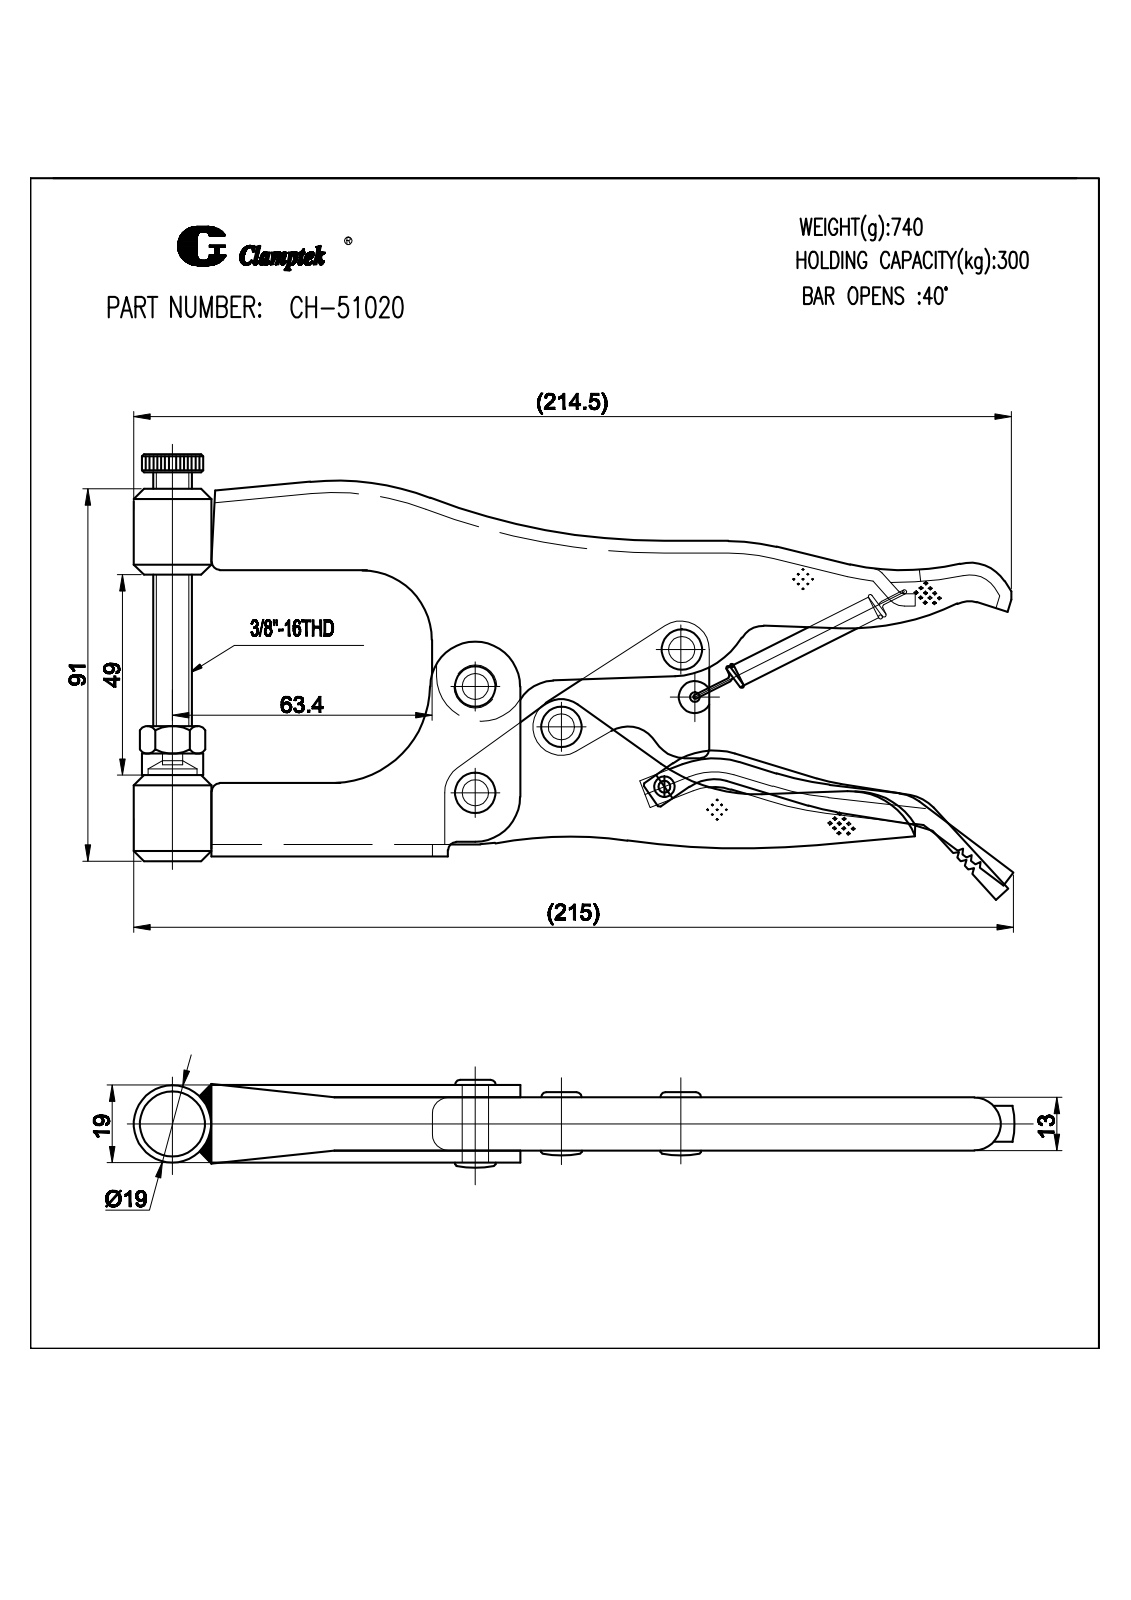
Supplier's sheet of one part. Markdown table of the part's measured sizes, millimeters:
| quantity | value |
| --- | --- |
| part name | CH-51020 |
| STEP written by | SolidWorks 2008 (CONFIG_CONTROL_DESIGN) |
| units | millimeters |
| bodies | 22 solids, 1247 faces (594 planar, 276 cylindrical, 377 other) |
| overall size | 212.8 × 112.51 × 22 |
| volume | 85 685 mm³ |
| surface area | 63 198 mm² |
| round holes (diameter × count) | 6.4 × 4, 5.63 × 2, 5.68 × 2, 19 × 2, 2.28 × 1, 2.33 × 1, 2.5 × 1, 3 × 1, 5.04 × 1, 6.5 × 1, 8.5 × 1, 12.04 × 1 |
| round bosses / shafts (diameter × count) | 10 × 4, 7 × 2, 6.3 × 2, 5 × 2, 15.04 × 1, 15 × 1, 10.5 × 1, 9.5 × 1 |
| partial cylindrical surfaces (radius × count) | 3.5 × 9, 6.5 × 9, 1 × 4, 2 × 3, 11 × 3, 0.5 × 2, 3 × 2, 6 × 2 |
| main face-to-face distances | 3, 10, 13, 7, 6, 16, 19, 1, 4, 12 |
| hole center spacings | 11.03, 12.11, 18.27, 23.27, 23.28, 25.86, 26, 26.5 |
